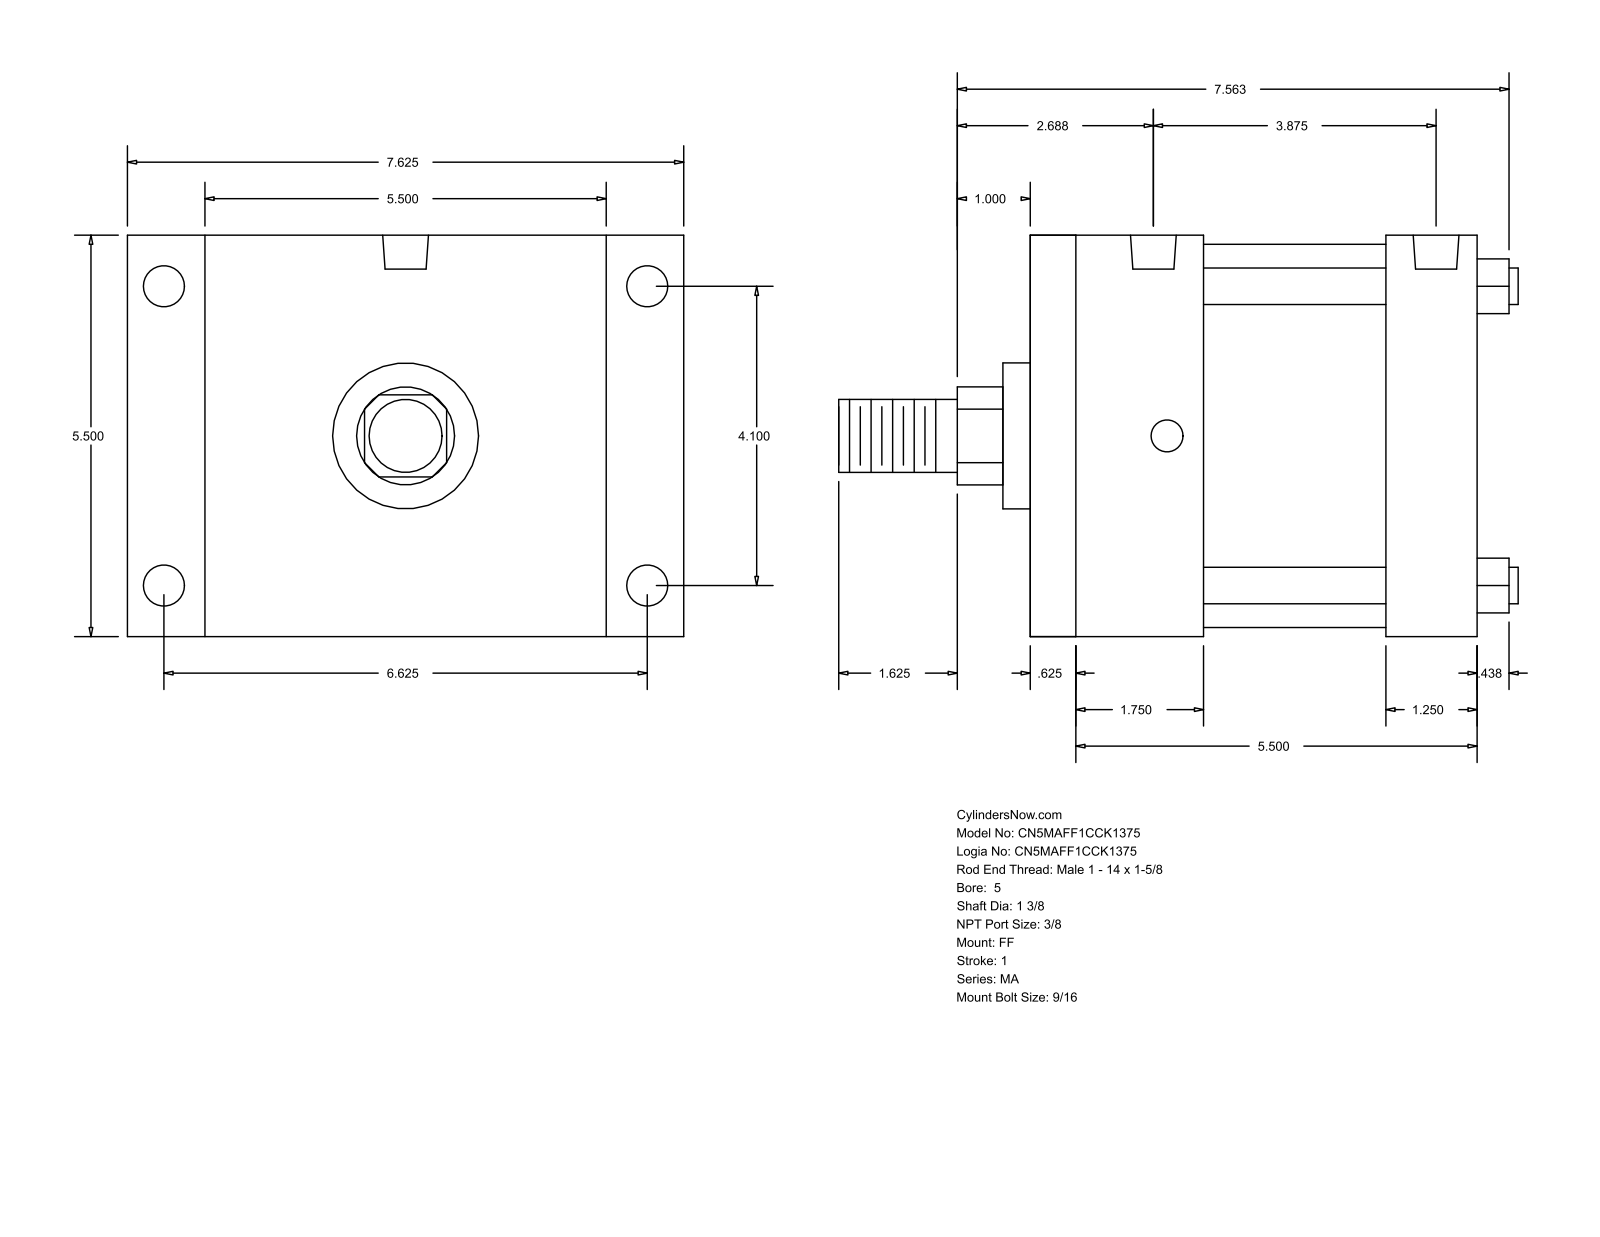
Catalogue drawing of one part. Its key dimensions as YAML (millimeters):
part_name: "MA_FF__0500_1.375"
step_written_by: "GSSL Pune (CONFIG_CONTROL_DESIGN)"
units: millimeters
bodies: {solids: 0, faces: 92, planar: 64, cylindrical: 28, other: 0}
overall_size: [236.54, 193.68, 139.7]
round_holes:
  - {diameter: 11.11, count: 4}
  - {diameter: 14.29, count: 4}
  - {diameter: 15.93, count: 2}
round_bosses_or_shafts:
  - {diameter: 12.7, count: 4}
  - {diameter: 133.35, count: 1}
  - {diameter: 50.8, count: 1}
  - {diameter: 34.92, count: 1}
  - {diameter: 25.4, count: 1}
partial_cylinders:
  - {radius: 17.06, count: 1}
face_to_face_distances: [139.7, 155.57, 15.87, 166.69, 123.82, 107.95, 31.75, 60.32, 44.45, 63.5]
hole_center_spacings: [88.9, 104.14, 168.28, 197.9, 4.76, 4.77, 93.66, 93.67]
